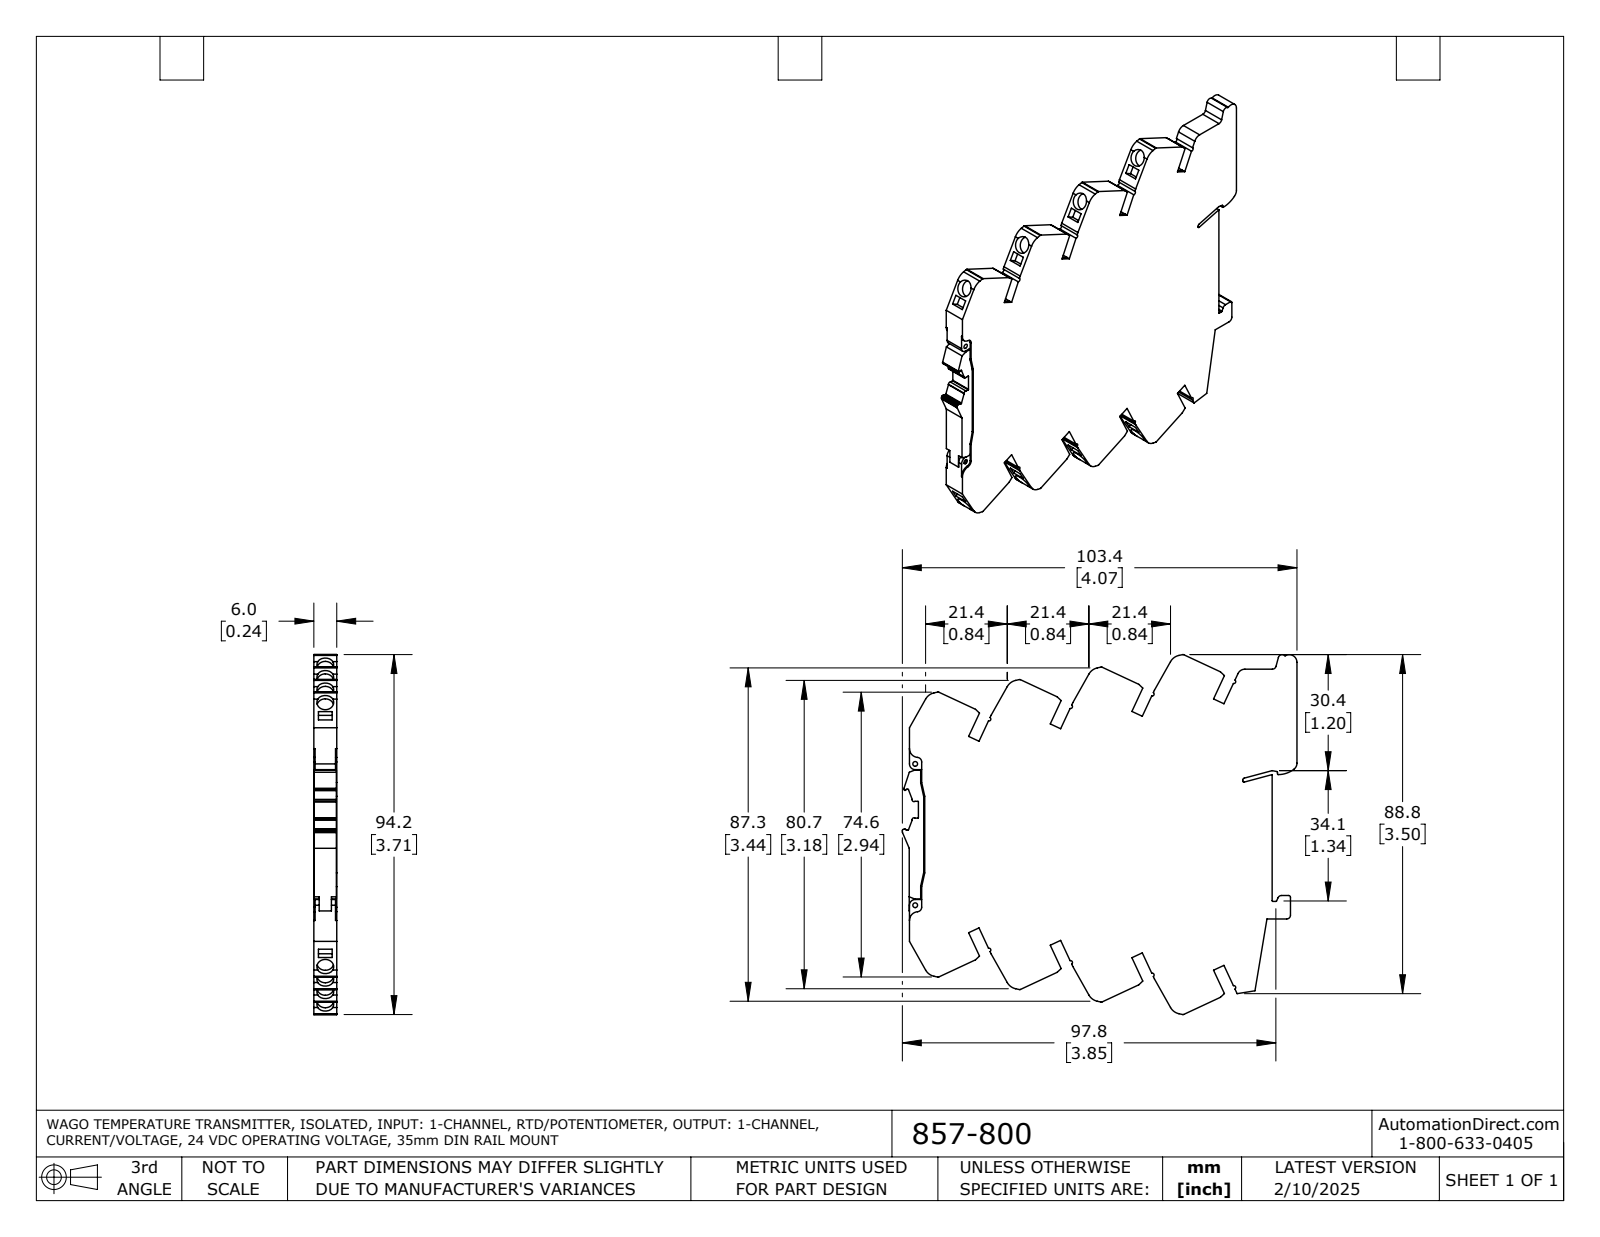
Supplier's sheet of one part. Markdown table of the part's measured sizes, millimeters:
| quantity | value |
| --- | --- |
| part name | 857-800 |
| STEP written by | SolidWorks 2021 (AUTOMOTIVE_DESIGN) |
| units | millimeters |
| bodies | 1 solid, 317 faces (219 planar, 98 cylindrical, 0 other) |
| overall size | 103.4 × 94.3 × 6 |
| volume | 43 930 mm³ |
| surface area | 19 260 mm² |
| round holes (diameter × count) | 4.4 × 8, 1.2 × 2 |
| partial cylindrical surfaces (radius × count) | 0.5 × 12, 0.2 × 11, 0.4 × 8, 3.4 × 8, 1 × 4, 0.3 × 3, 2 × 3, 0.5 × 2 |
| main face-to-face distances | 6, 18, 17, 12, 5.9, 12, 3, 24, 36, 6.5 |
| hole center spacings | 13.4, 13.3, 26.7, 26.7, 26.7, 37, 40, 40.1 |
